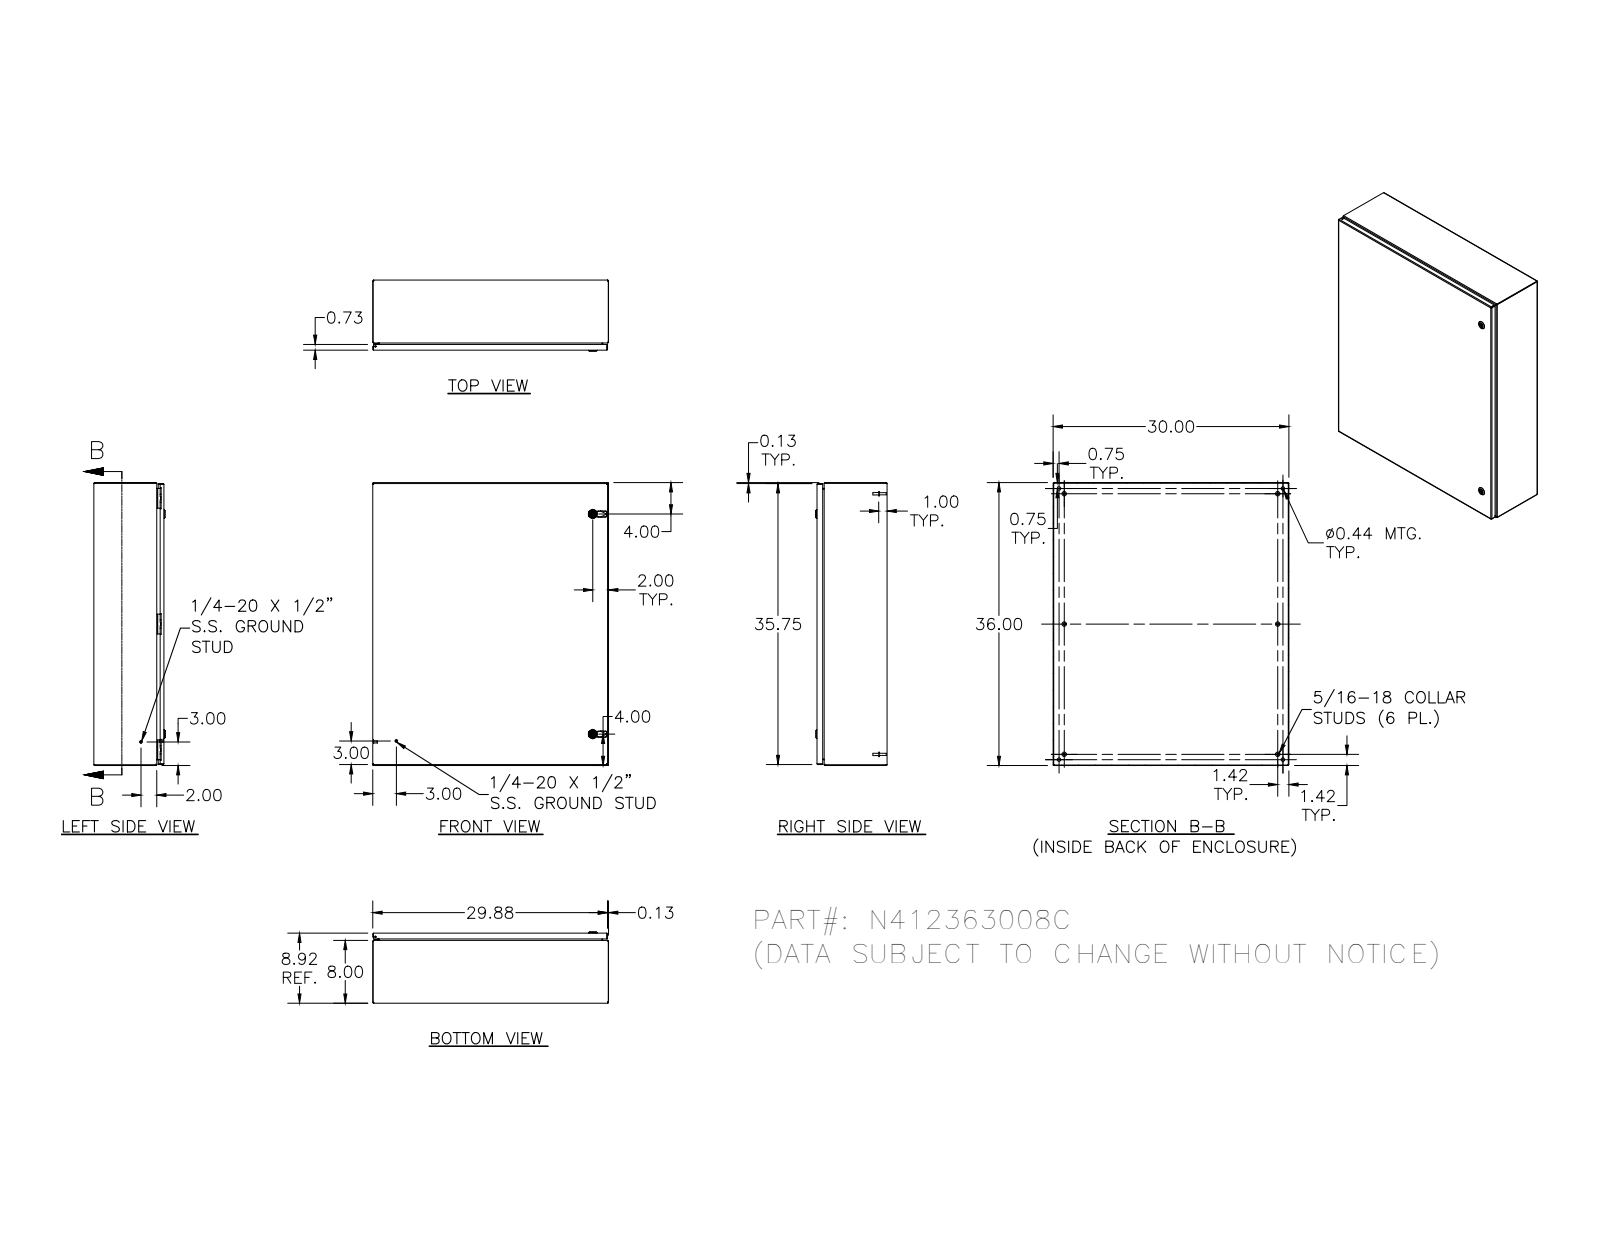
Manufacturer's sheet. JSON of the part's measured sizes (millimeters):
{"part_name": "N412363008C; N4123630CLID; 35124; 1000-u155_asm (+8 more)", "step_written_by": "Autodesk Inventor 2011 (AUTOMOTIVE_DESIGN)", "units": "millimeters", "bodies": {"solids": 49, "faces": 2252, "planar": 831, "cylindrical": 856, "other": 565}, "overall_size": [914.4, 762, 230.5], "volume_mm3": 4226000, "surface_area_mm2": 4524000, "round_holes": [[4.8, 7], [2.4, 6], [3.9, 6], [4.2, 6], [4.4, 6], [11.1, 4], [4, 3], [5, 2], [8, 2], [10, 2], [10.2, 2], [16.1, 2]], "round_bosses_or_shafts": [[6.4, 14], [14.3, 6], [9.1, 6], [8.1, 6], [7.6, 6], [7, 6], [6.5, 6], [4.2, 6]], "partial_cylinders_radius": [[0.3, 54], [1.3, 38], [0.8, 34], [0.4, 26], [3.2, 24], [0.5, 23], [2.7, 20], [0.8, 12]], "face_to_face_distances": [1.9, 224.6, 222.7, 226.5, 1.9, 760.1, 758.2, 760.1, 762, 910.6], "hole_center_spacings": [406.4, 812.8, 16.8, 16.7, 33.2, 49.9, 406.6, 12.7]}
